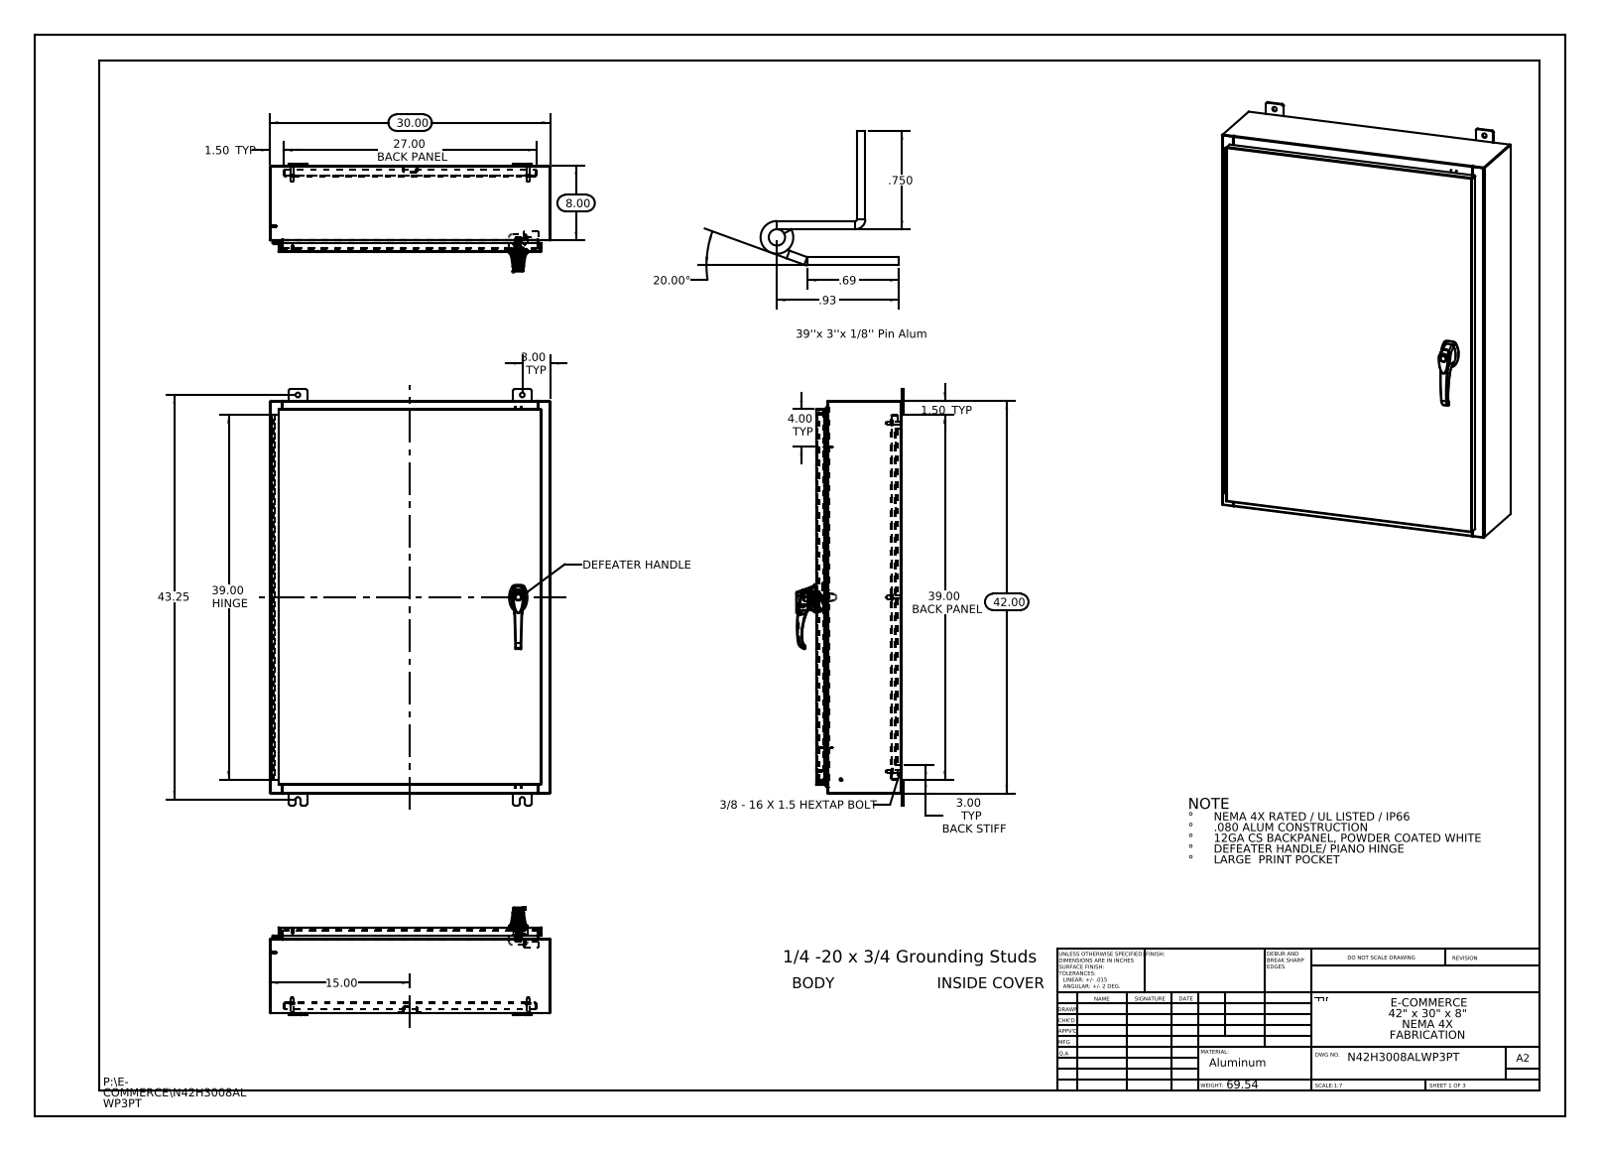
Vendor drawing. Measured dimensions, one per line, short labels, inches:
name: 297025; N42H3008ALWP3PT 263033_Industrilas; 2616310101; N42H3008ALWP3PT Defeater Handle Rod (+8 more)
written by: SolidWorks 2013 (CONFIG_CONTROL_DESIGN)
unit: in
bodies: 40 solids, 3038 faces (1155 planar, 1165 cylindrical, 718 other)
size: 44.5 × 30 × 11.495
volume: 446.2 in³; area: 11 005 in²
holes: 10× ⌀0.5, 4× ⌀0.25, 3× ⌀0.138, 3× ⌀0.161, 2× ⌀0.079, 2× ⌀0.203, 2× ⌀0.313, 2× ⌀0.437, 1× ⌀0.125, 1× ⌀0.125, 1× ⌀0.197, 1× ⌀0.276
bosses: 6× ⌀0.625, 6× ⌀0.375, 6× ⌀0.33, 4× ⌀0.157, 4× ⌀0.14, 3× ⌀0.315, 3× ⌀0.236, 1× ⌀1.181
rounds: 37× R0.118, 33× R0.006, 28× R0.013, 24× R0.19, 22× R0.088, 15× R0.039, 12× R0.028, 6× R0.008
face distances: 0.075, 9.126, 9.051, 0.104, 9.201, 1, 8.126, 1.075, 8.051, 1.179
hole spacings: 14.36, 16.667, 18.625, 31.376, 25.25, 0.295, 0.625, 0.841
